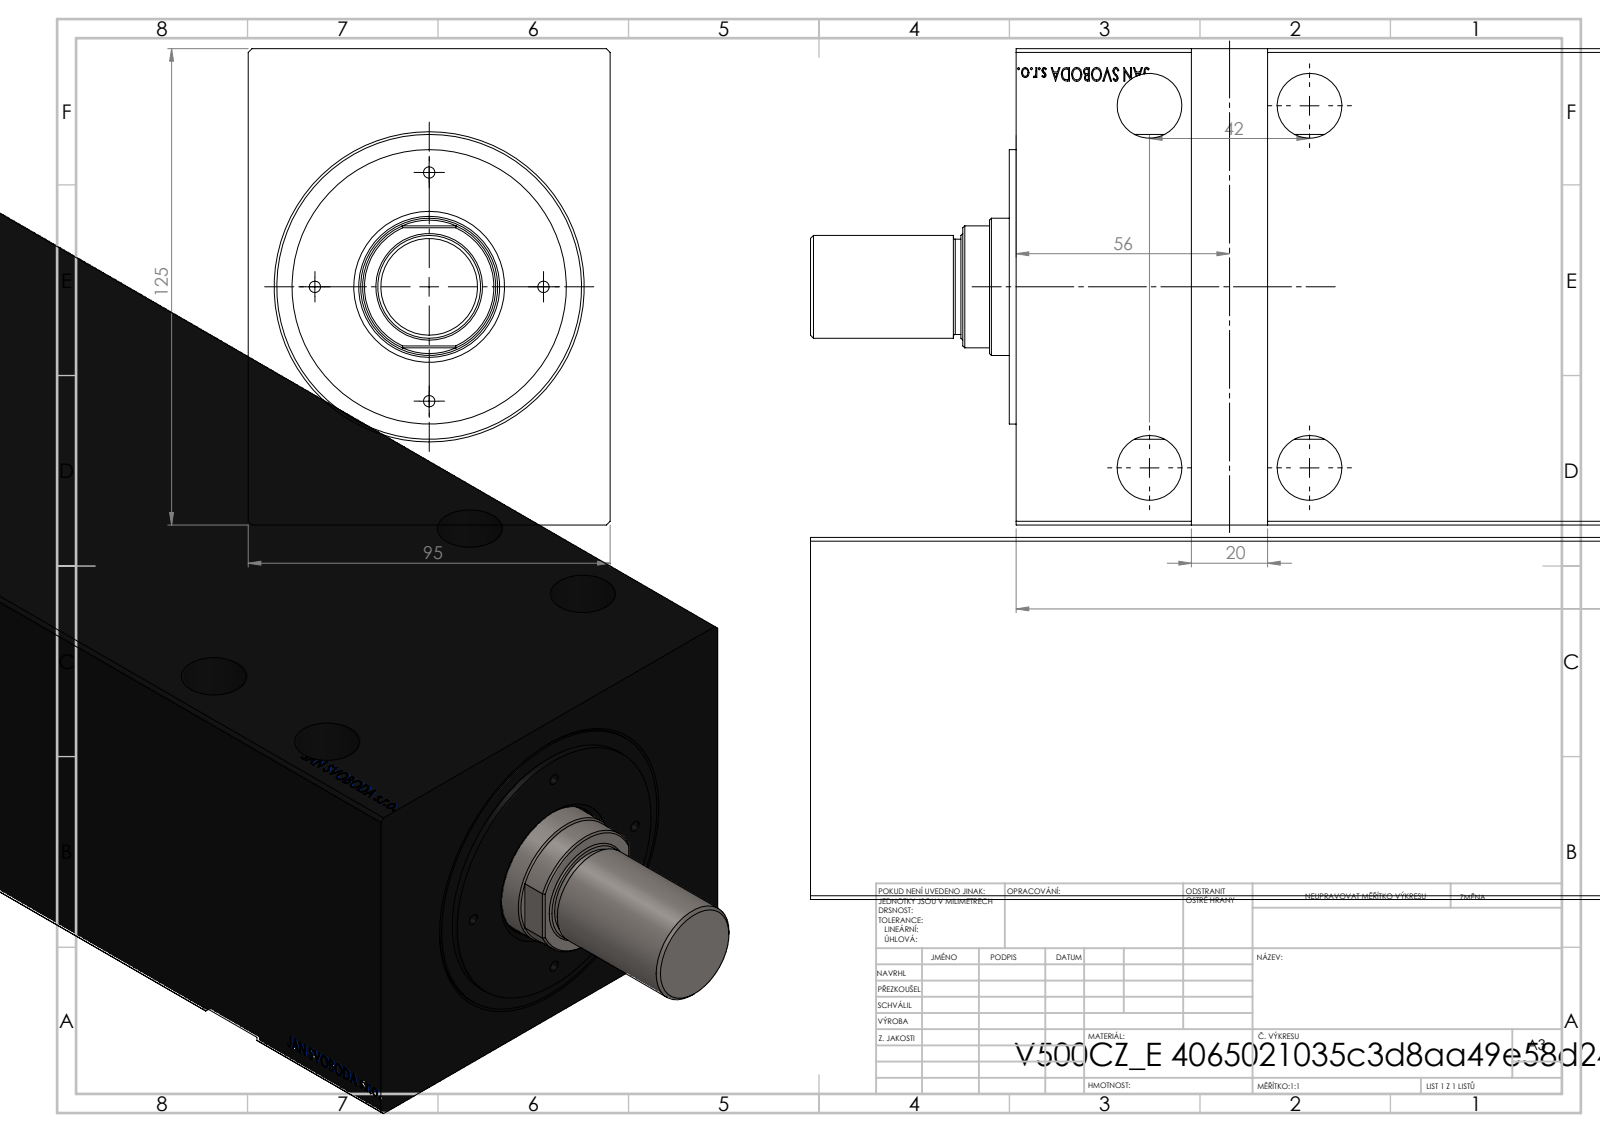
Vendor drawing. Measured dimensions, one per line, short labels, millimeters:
written by: SolidWorks 2019 (CONFIG_CONTROL_DESIGN)
unit: mm
bodies: 1 solid, 794 faces (387 planar, 25 cylindrical, 382 other)
size: 341 × 125 × 95
volume: 2 901 000 mm³; area: 253 178 mm²
holes: 4× ⌀17, 2× ⌀5.5, 2× ⌀20, 2× ⌀26.5, 1× ⌀36, 1× ⌀63, 1× ⌀80
face distances: 95, 125, 341, 280.25, 60.75, 2, 93, 91, 189.25, 250
hole spacings: 42, 95, 103.87, 308
